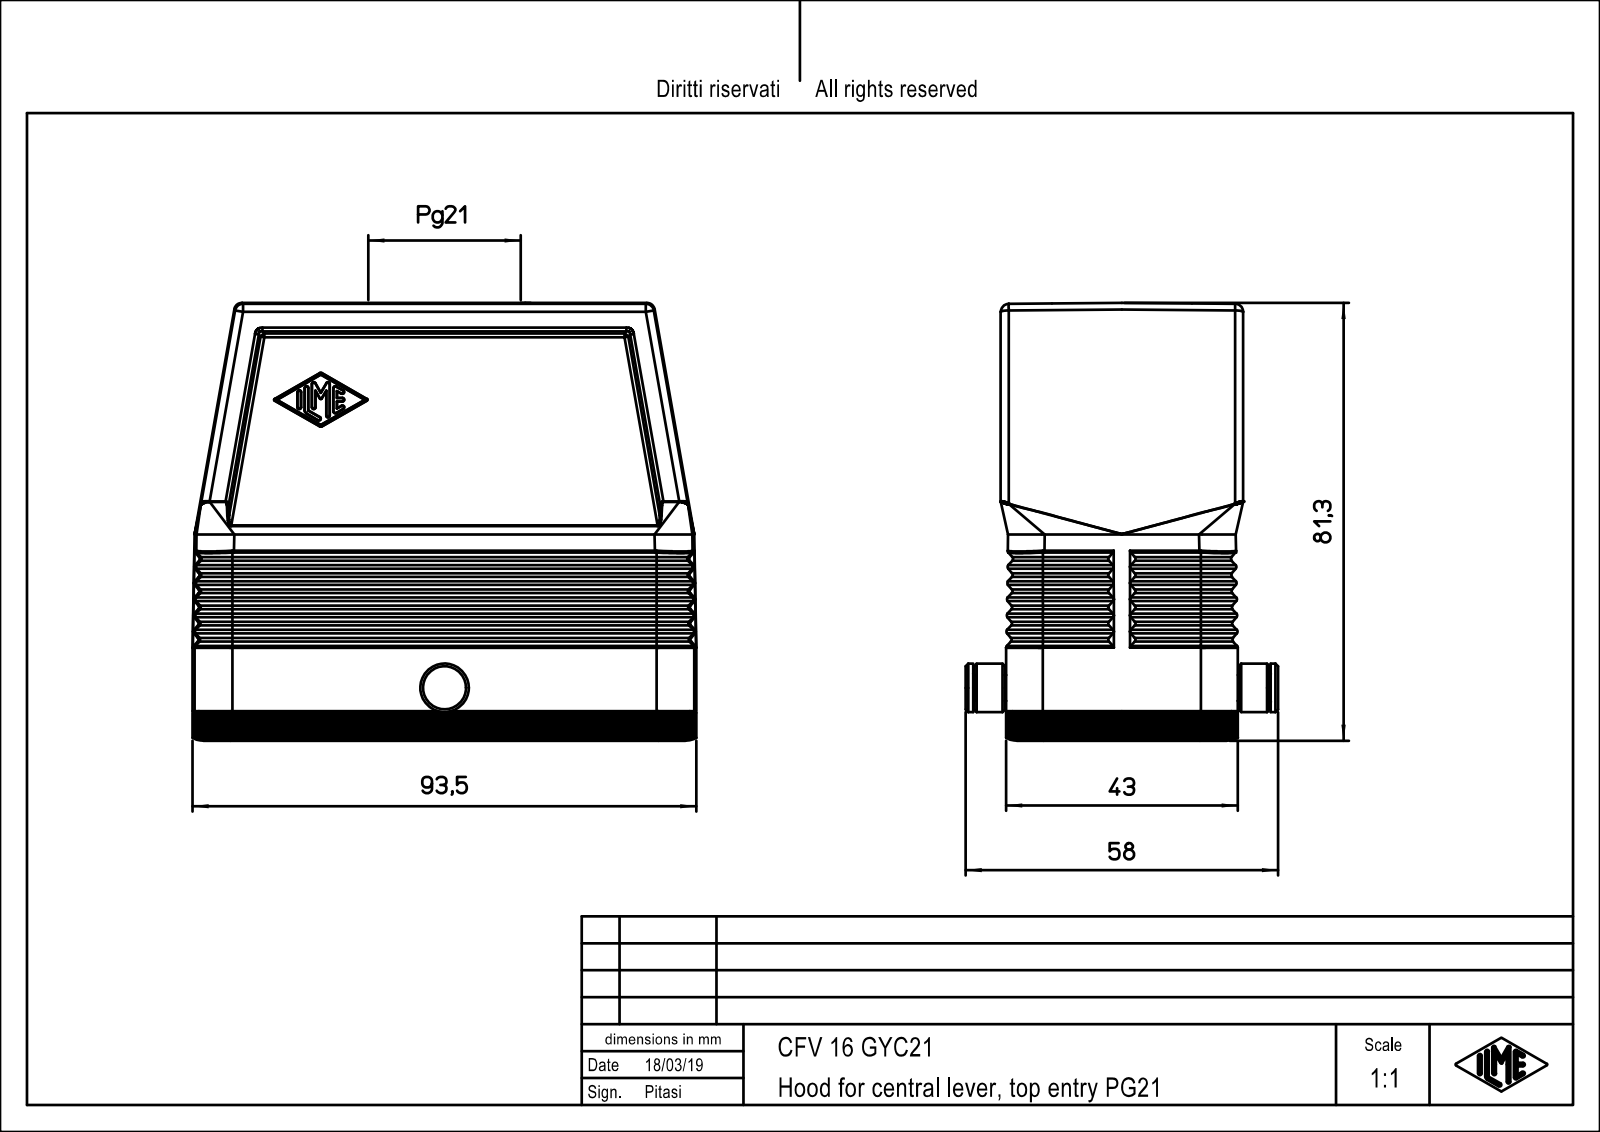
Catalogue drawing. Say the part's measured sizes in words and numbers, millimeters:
The part is named "CFV_16_GYC21". Its 3-D file was written by "PTC Creo Elements/Direct Modeling 19.0E 27-Jun-2016 (C) Parametric Technology GmbH (AUTOMOTIVE_DESIGN)". It is 1 solid with 577 faces: 223 planar, 174 cylindrical and 180 other. Overall it measures 93.5 by 81.25 by 58 millimeters. Its volume is 104 270 cubic millimeters and its surface area 47 576 square millimeters. Round holes: 1 of diameter 27.54. Round bosses or shafts: 1 of diameter 9, 1 of diameter 4.8. Partial cylindrical surfaces (rounded edges, fillets, slot ends): 84 of radius 0.5, 16 of radius 1, 12 of radius 7, 10 of radius 1.5, 8 of radius 3, 4 of radius 3.5, 4 of radius 4, 4 of radius 4.2. The main face-to-face distances are 43, 1.01, 4, 2, 7, 6, 1, 44, 39, 5.
